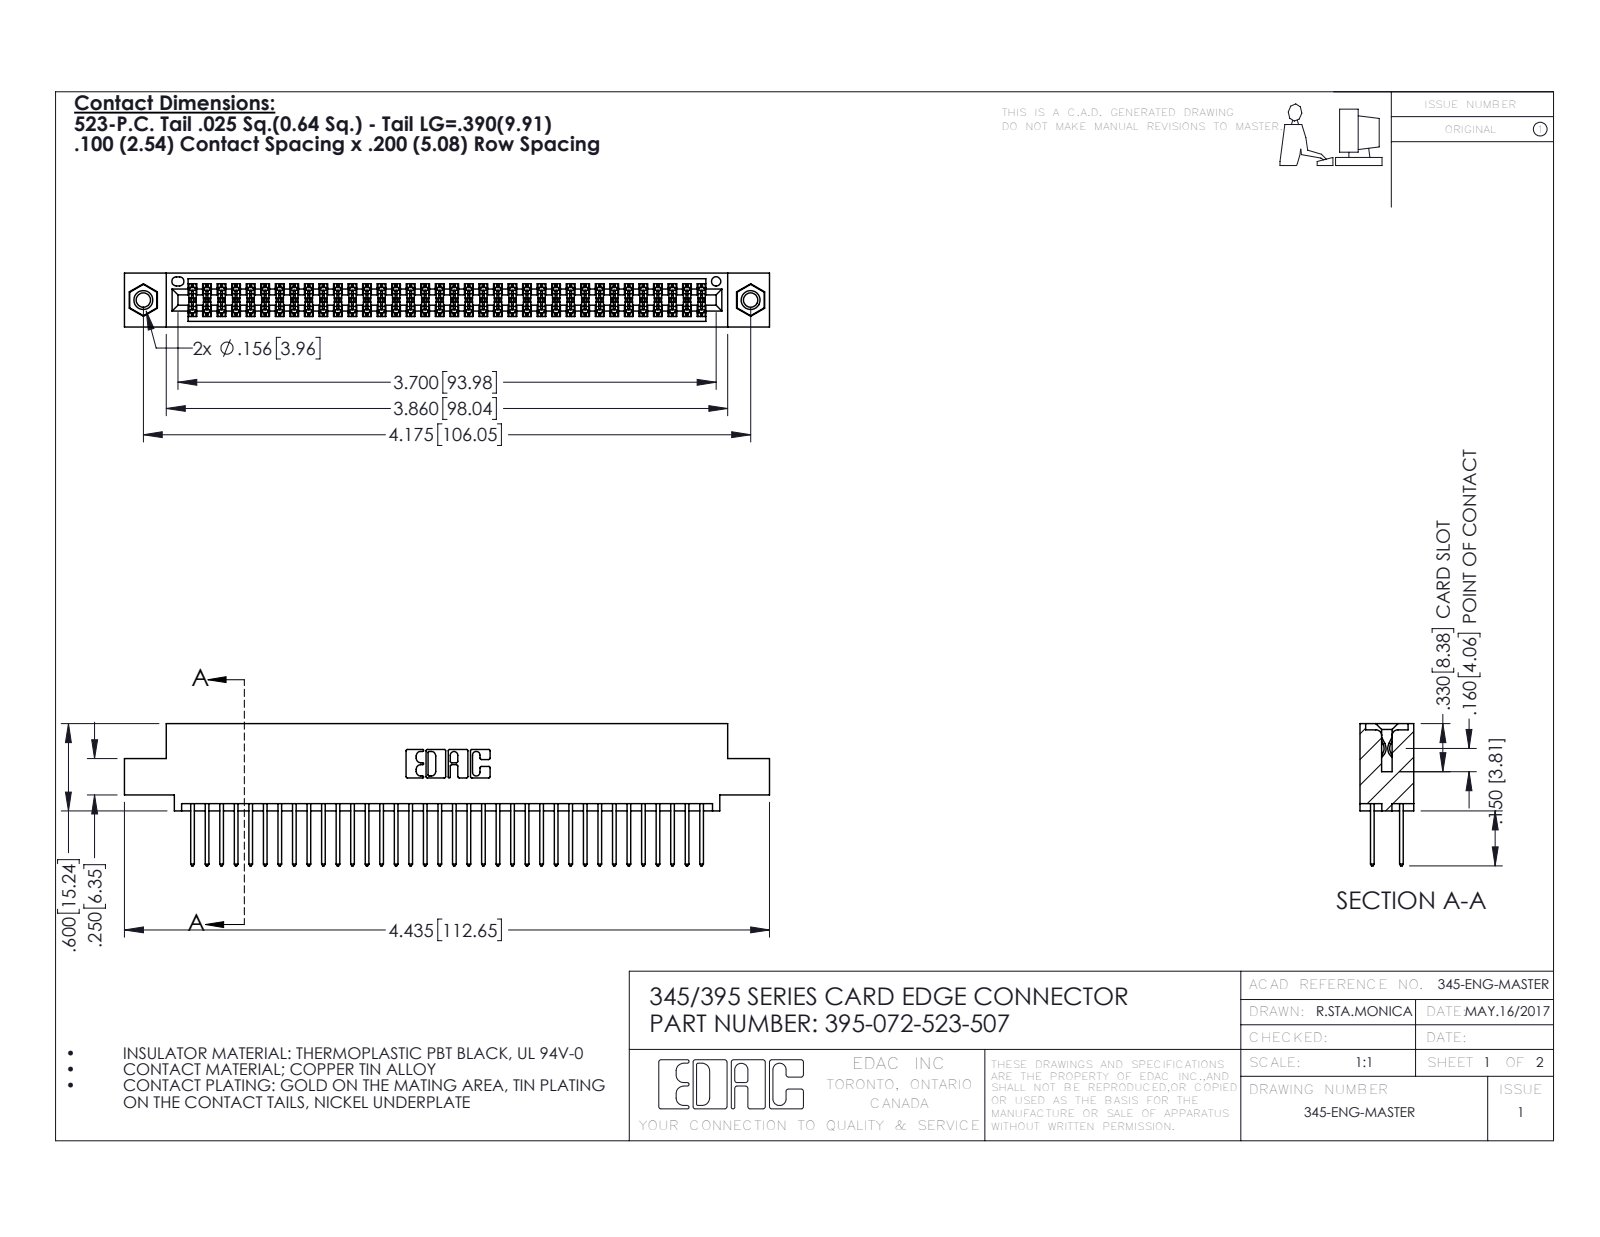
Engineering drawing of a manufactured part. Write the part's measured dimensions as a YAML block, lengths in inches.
part_name: "345-292-001_345-293-123; 345 Part_0.110 Offset - 0.156 Dia-TI; 395-072-523-507; 345-250-001_345-250-005-103"
step_written_by: "SolidWorks 2016 (CONFIG_CONTROL_DESIGN)"
units: inches
bodies: {solids: 75, faces: 3790, planar: 2492, cylindrical: 1282, other: 16}
overall_size: [4.435, 0.977, 0.37]
volume: 0.668
surface_area: 26.12
round_holes:
  - {diameter: 0.098, count: 2}
  - {diameter: 0.125, count: 2}
  - {diameter: 0.156, count: 2}
  - {diameter: 0.064, count: 1}
round_bosses_or_shafts:
  - {diameter: 0.155, count: 2}
partial_cylinders:
  - {radius: 0.006, count: 108}
  - {radius: 0.01, count: 72}
  - {radius: 0.01, count: 22}
  - {radius: 0.007, count: 6}
  - {radius: 0.031, count: 6}
  - {radius: 0.026, count: 3}
  - {radius: 0.014, count: 2}
  - {radius: 0.019, count: 2}
face_to_face_distances: [0.072, 0.298, 0.2, 0.098, 0.272, 0.025, 0.37, 0.225, 0.175, 0.149]
hole_center_spacings: [0.27, 3.939, 4.175]
